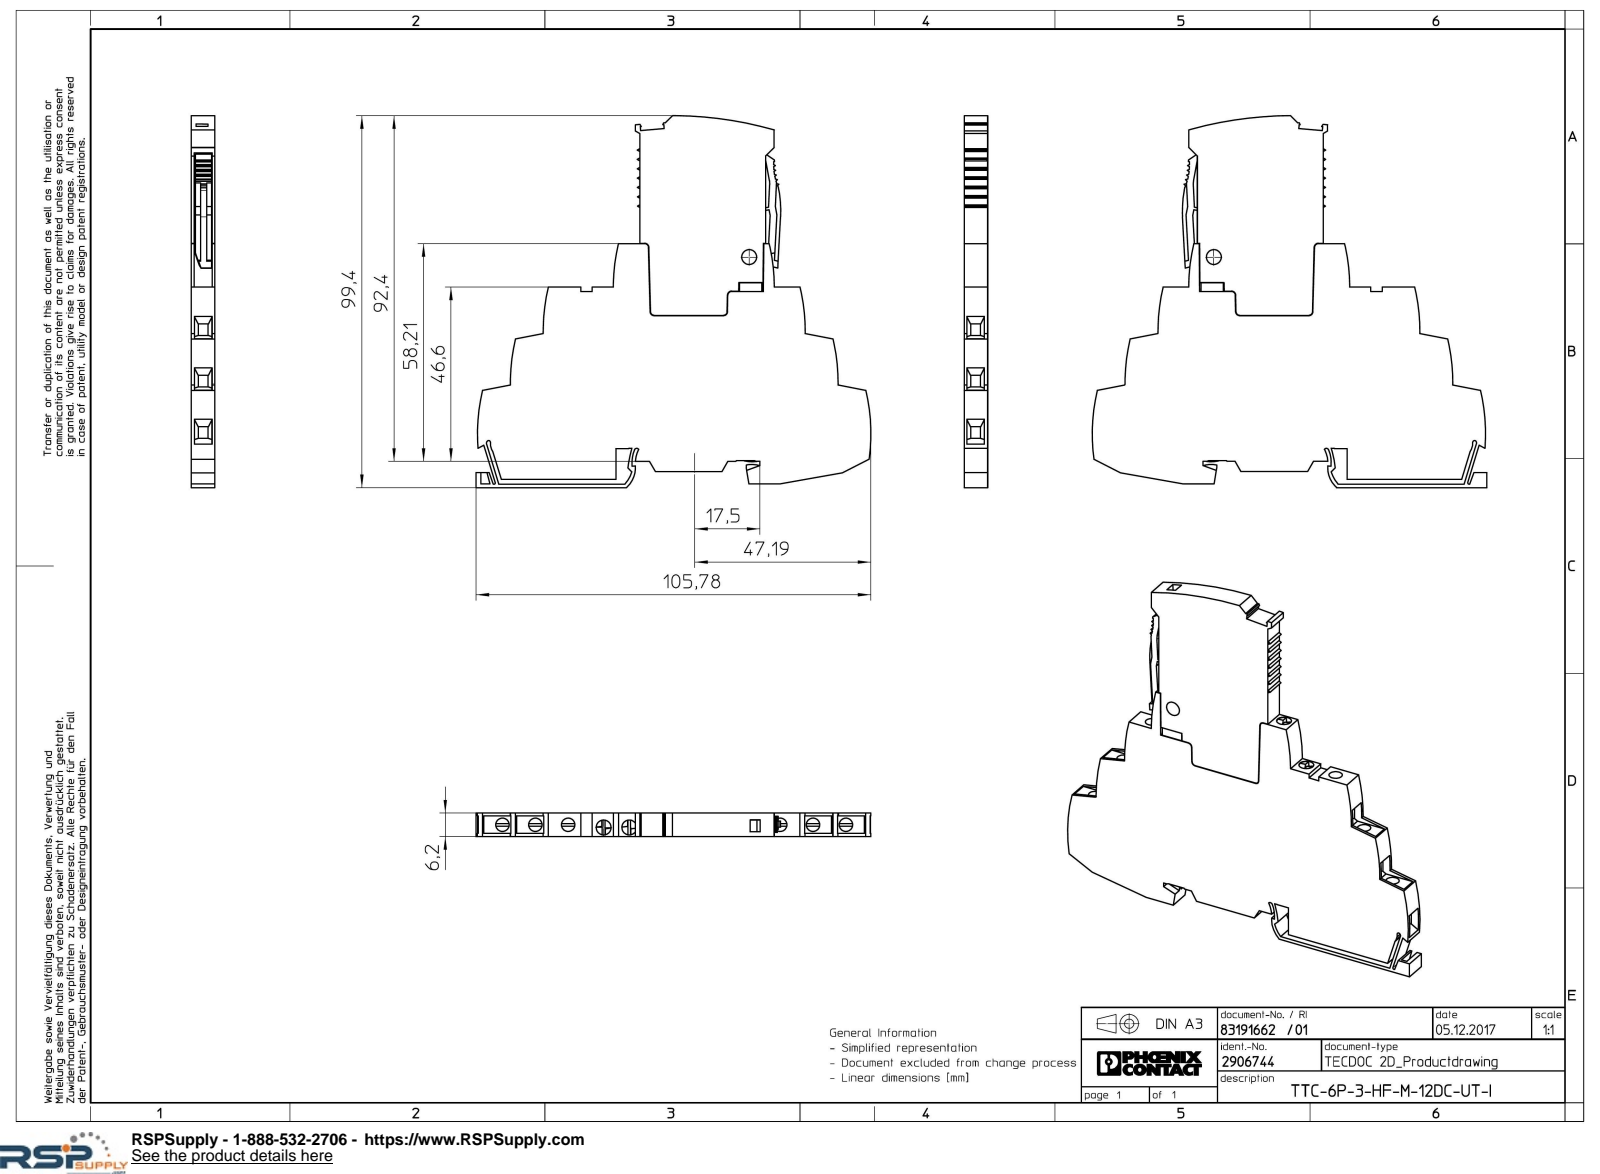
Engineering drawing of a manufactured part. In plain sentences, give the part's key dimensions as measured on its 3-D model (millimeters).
The part is named "TTC_6P...M...UT_I-select". Its 3-D file was written by "Creo Elements/Direct Modeling 20.1A 29-Sep-2018 (C) Parametric Technology GmbH (AUTOMOTIVE_DESIGN)". It is 1 solid with 372 faces: 297 planar, 67 cylindrical and 8 other. Overall it measures 105.78 by 99.4 by 6.3 millimeters. Its volume is 37 600 cubic millimeters and its surface area 17 603 square millimeters. Round holes: 6 of diameter 3.6, 1 of diameter 4. Partial cylindrical surfaces (rounded edges, fillets, slot ends): 8 of radius 50, 4 of radius 0.5, 4 of radius 1, 2 of radius 0.9, 2 of radius 1.1, 2 of radius 7.5, 1 of radius 0.2, 1 of radius 0.3. The main face-to-face distances are 6.3, 0.9, 2.17, 13.75, 3.65, 1.05, 1.27, 2.6, 4.38, 1.92. The hole center spacings are 8.8, 74.4, 17.6, 65.6, 83.2, 56.8, 92.
